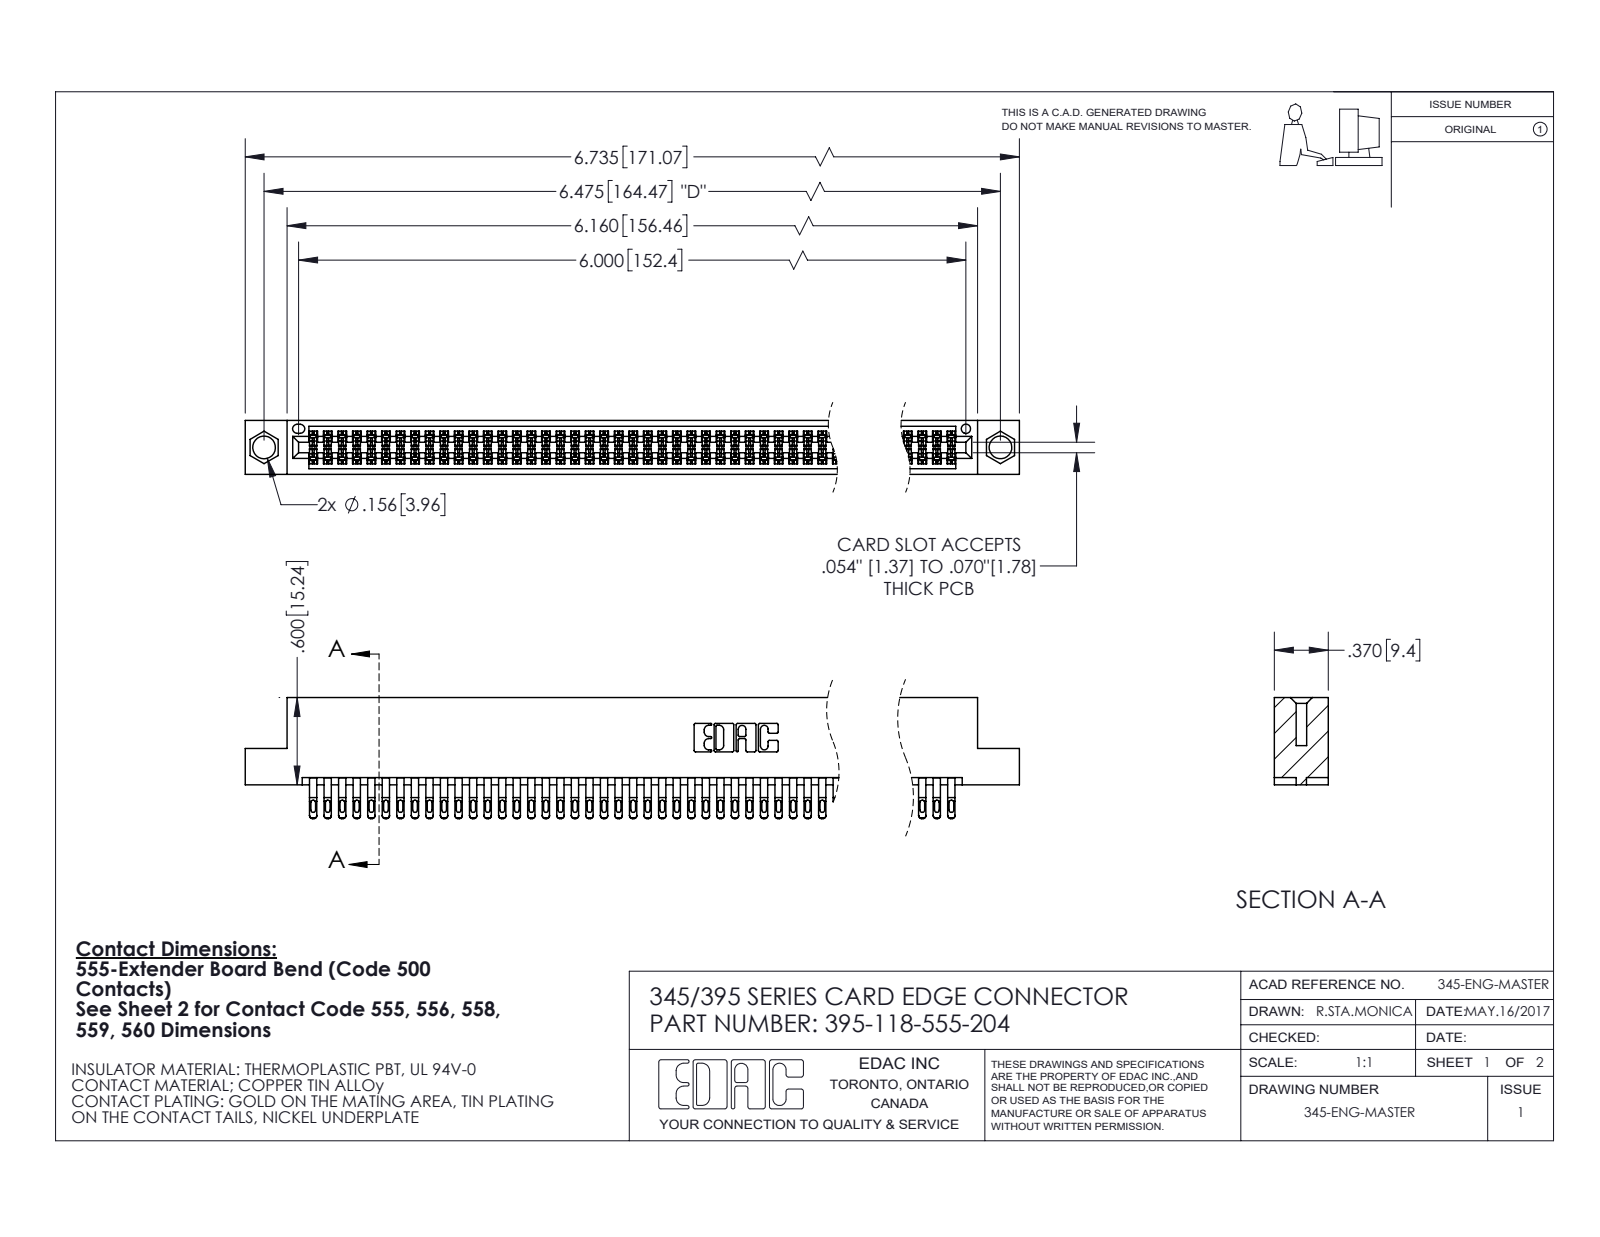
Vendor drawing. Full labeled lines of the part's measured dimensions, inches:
Part name (STEP PRODUCT): 345-292-001_555 Tail; 345 Part_Flush Mounting Lugs - 0.156 Dia-TI; 395-118-555-204
STEP written by: SolidWorks 2020 (CONFIG_CONTROL_DESIGN)
Units: inches
Bodies: 119 solids, 6748 faces (3752 planar, 2996 cylindrical, 0 other)
Overall size (bounding box): 6.735 × 0.832 × 0.37
Volume: 1.038 in³ · Surface area: 41.1 in²
Round holes (diameter × count): ⌀0.156 ×2, ⌀0.064 ×1
Partial cylindrical surfaces — rounded edges, fillets, slot ends (radius × count): R0.016 ×295, R0.006 ×236, R0.02 ×236, R0.01 ×22, R0.007 ×6, R0.031 ×6, R0.026 ×3, R0.01 ×2
Main face-to-face distances: 0.298, 0.072, 0.025, 0.37, 0.2, 0.098, 0.272, 0.225, 0.175, 0.149
Hole centre spacings: 0.27, 6.239, 6.475
